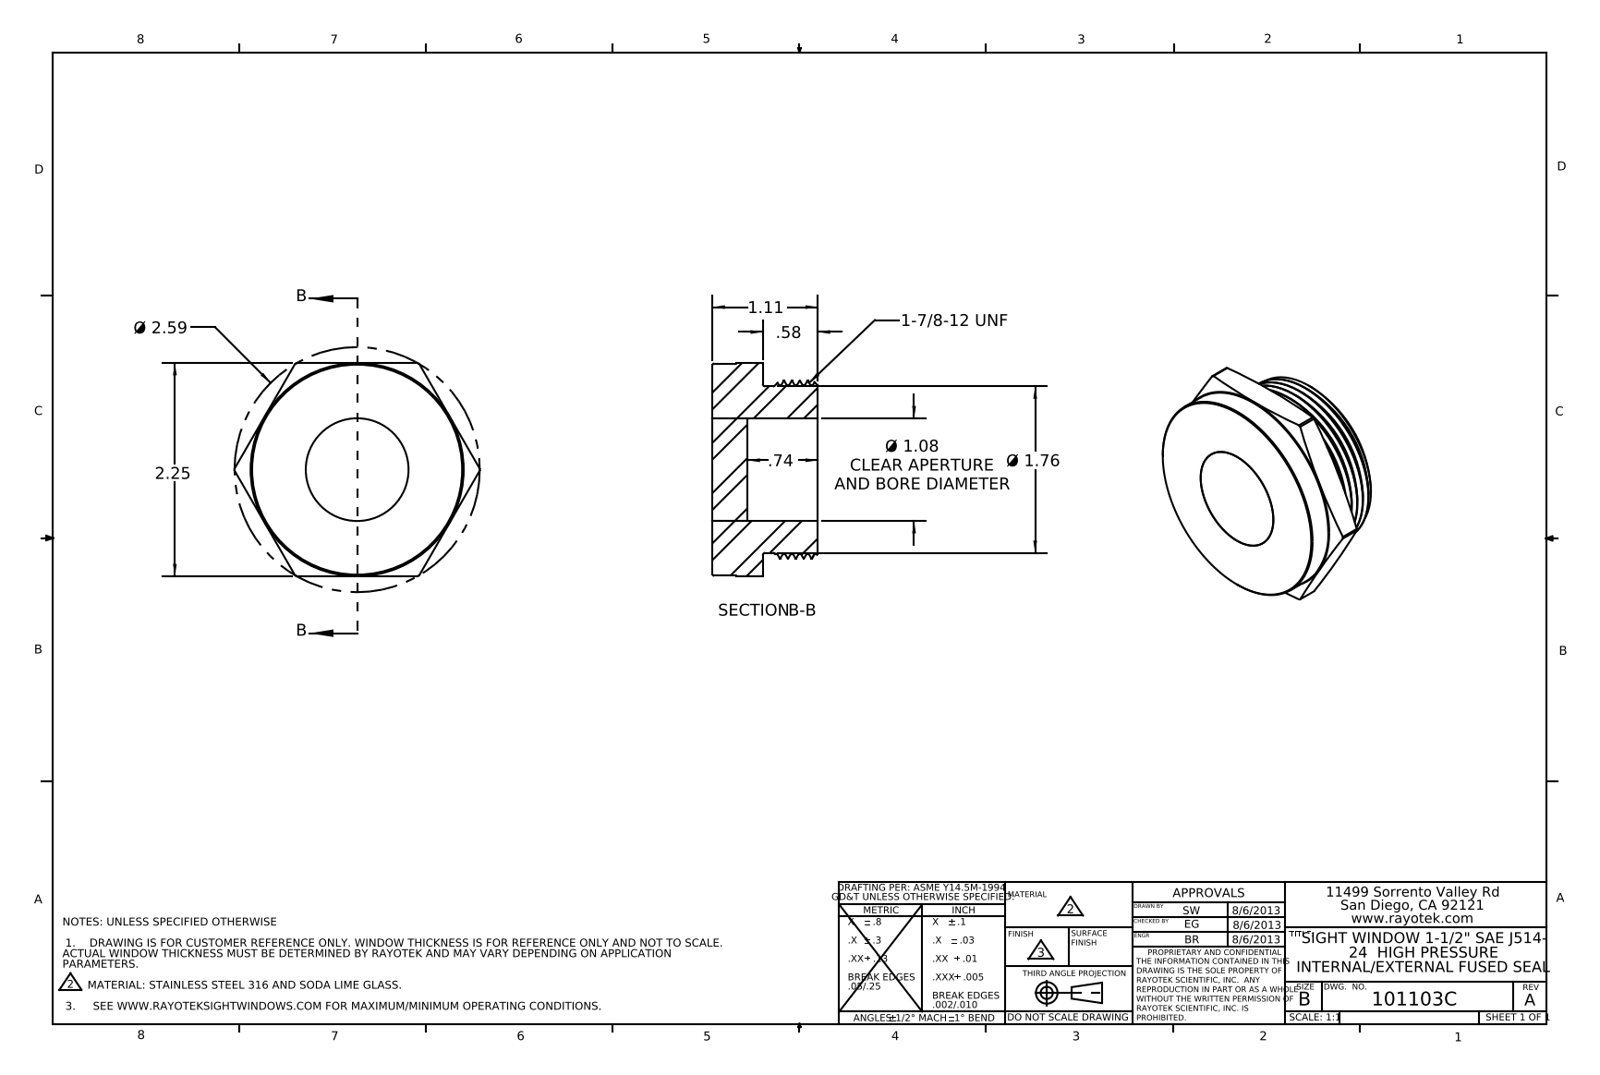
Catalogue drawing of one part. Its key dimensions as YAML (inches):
part_name: "403103"
step_written_by: "SolidWorks 2012 (AUTOMOTIVE_DESIGN)"
units: inches
bodies: {solids: 2, faces: 56, planar: 11, cylindrical: 24, other: 21}
overall_size: [2.586, 2.25, 1.11]
volume: 2.993
surface_area: 22.46
round_holes:
  - {diameter: 1.084, count: 1}
round_bosses_or_shafts:
  - {diameter: 2.235, count: 1}
  - {diameter: 1.875, count: 1}
  - {diameter: 1.756, count: 1}
partial_cylinders:
  - {radius: 1.293, count: 1}
face_to_face_distances: [1.11, 0.58, 0.53, 0.74, 0.16, 0.37, 2.25, 2.25]
